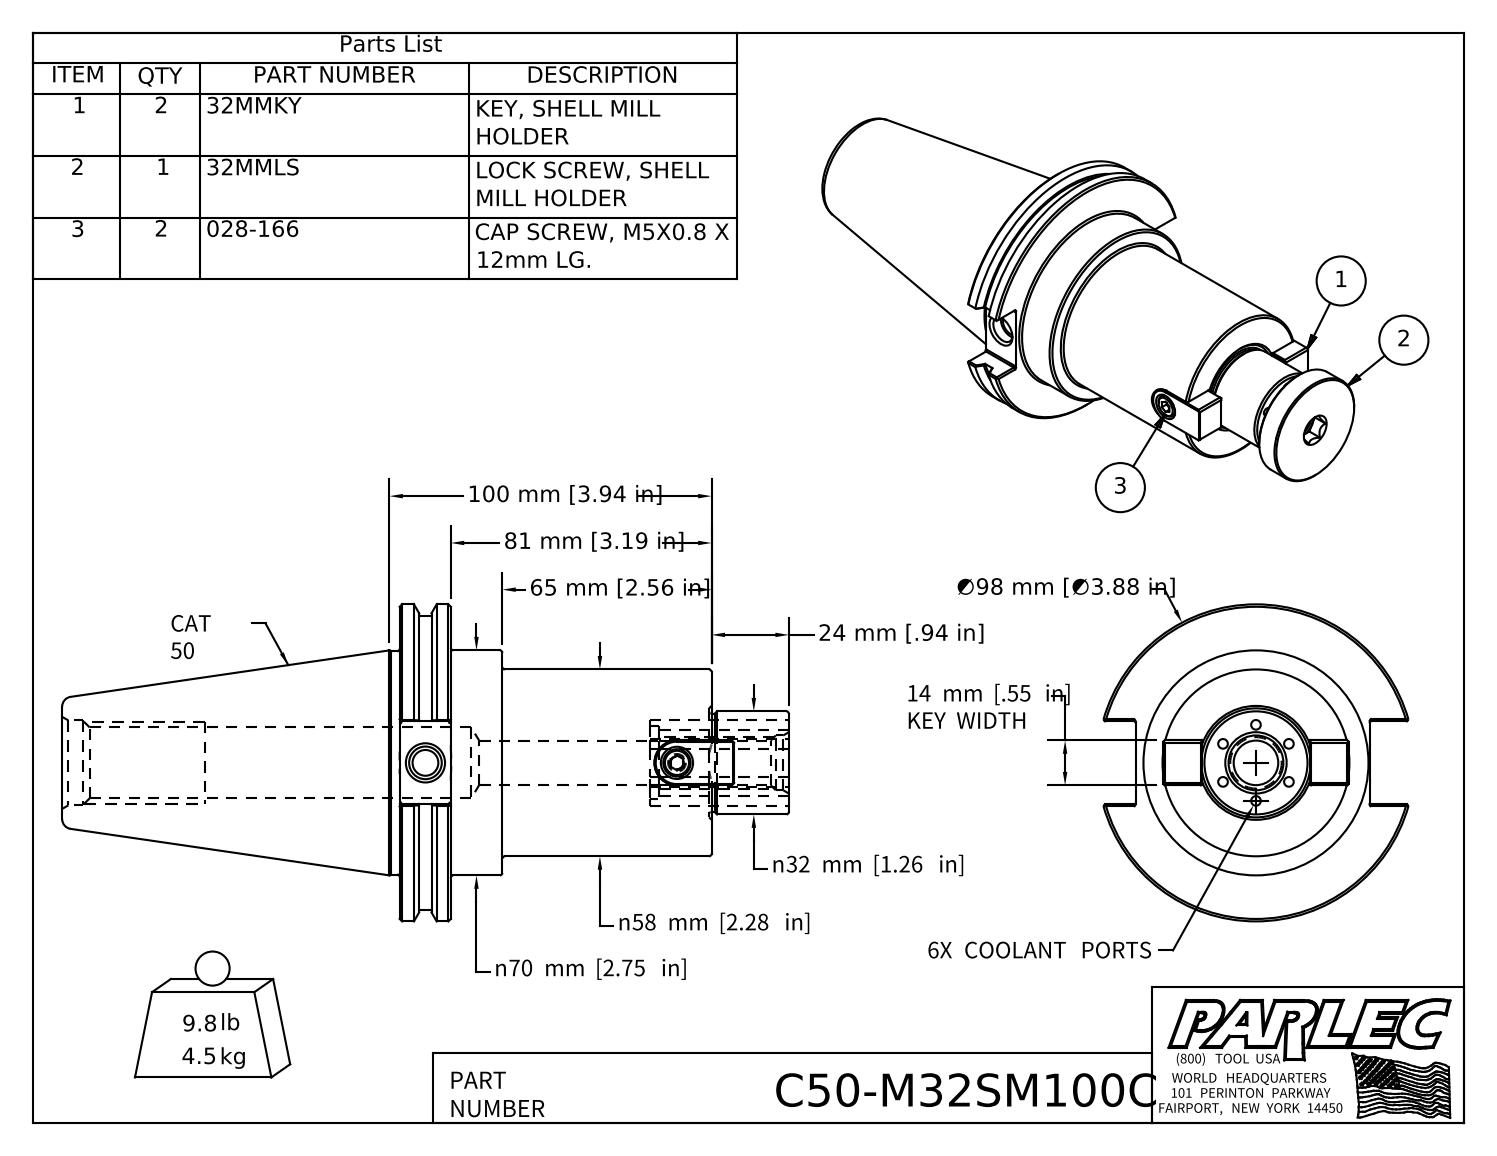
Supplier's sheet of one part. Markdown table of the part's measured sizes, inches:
| quantity | value |
| --- | --- |
| part name | C50-M32SM100C; 32MMKY; 028-166; 32MMLS |
| STEP written by | Autodesk Inventor 2022 (AUTOMOTIVE_DESIGN) |
| units | inches |
| bodies | 6 solids, 216 faces (106 planar, 59 cylindrical, 51 other) |
| overall size | 9.486 × 3.875 × 3.729 |
| volume | 34.64 in³ |
| surface area | 124.1 in² |
| round holes (diameter × count) | 0.118 × 6, 0.163 × 1, 0.217 × 1, 0.315 × 1, 0.394 × 1, 0.394 × 1, 0.399 × 1, 0.545 × 1, 0.67 × 1, 0.865 × 1, 1.038 × 1 |
| round bosses / shafts (diameter × count) | 3.875 × 1, 3.594 × 1, 2.75 × 1, 2.73 × 1, 2.283 × 1, 1.654 × 1, 1.26 × 1, 1.2 × 1 |
| partial cylindrical surfaces (radius × count) | 0.02 × 12, 0.275 × 1, 0.276 × 1, 0.45 × 1 |
| main face-to-face distances | 0.625, 3.812, 3.187, 4.736, 5.361, 1.549, 5.007, 4.382, 1.195, 0.354 |
| hole center spacings | 0.465, 0.806, 0.465, 0.93, 0.93, 3.074 |
